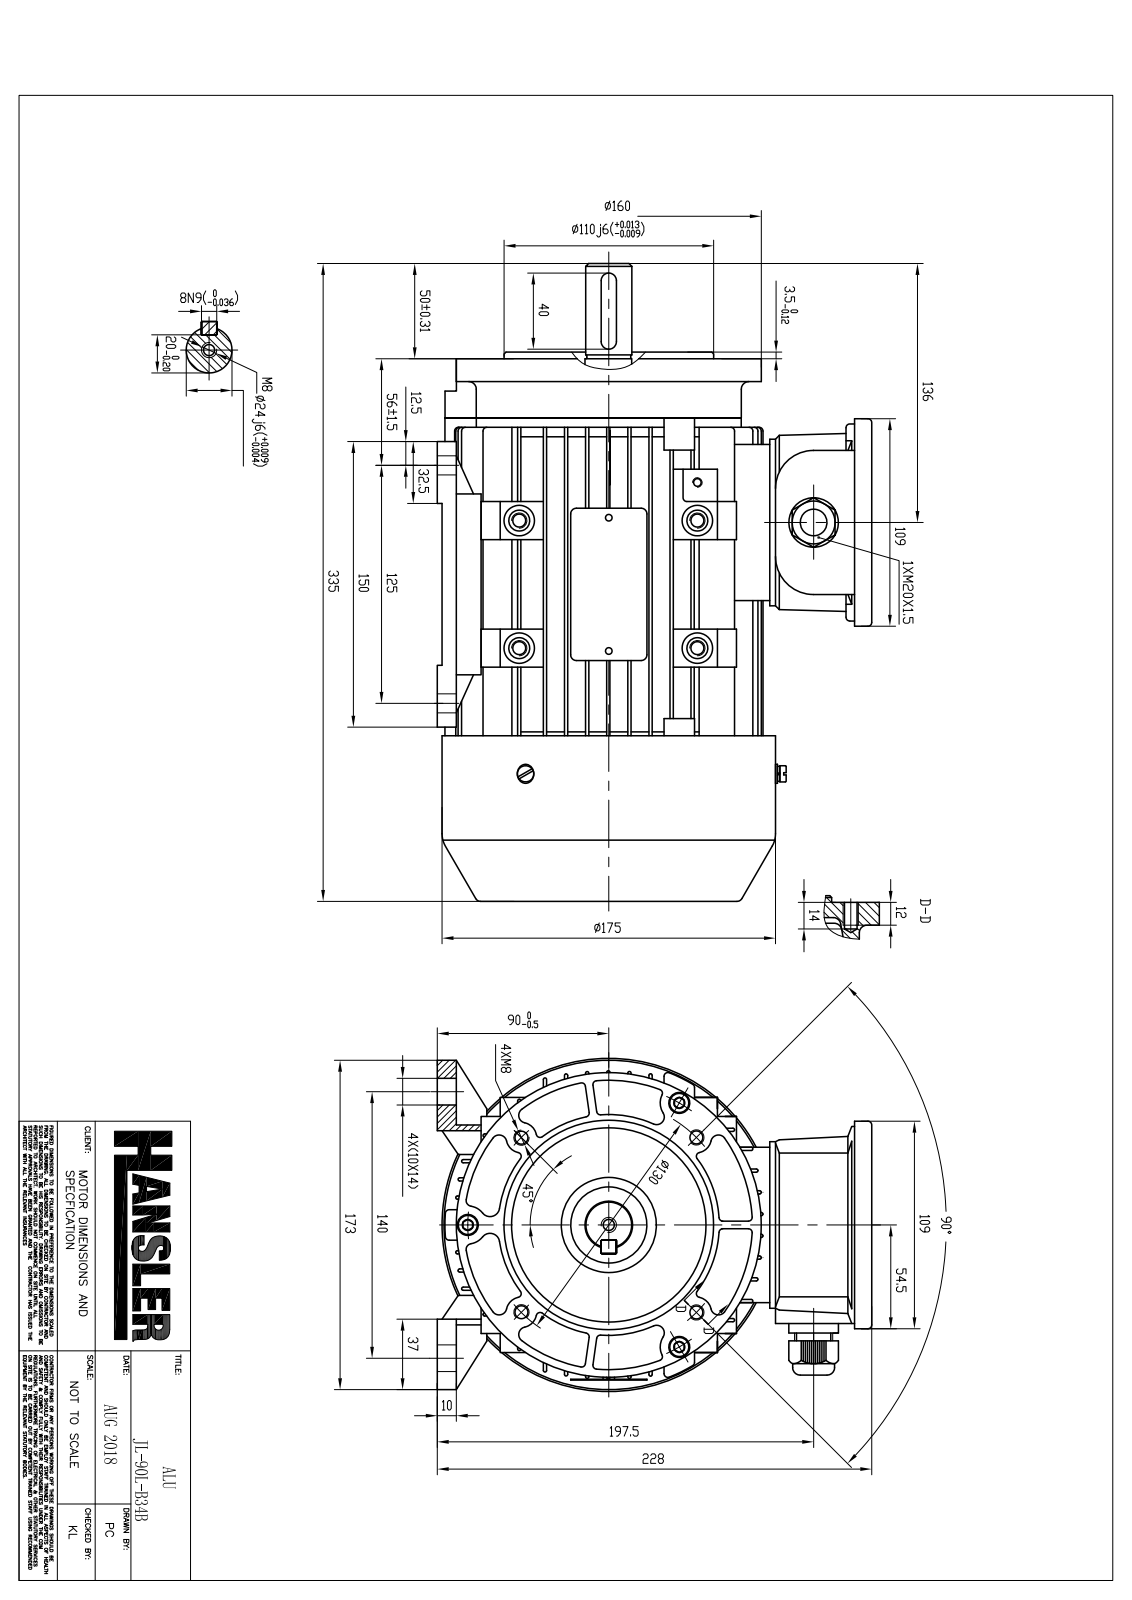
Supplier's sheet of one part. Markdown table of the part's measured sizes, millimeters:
| quantity | value |
| --- | --- |
| part name | JL-90L-B34B |
| STEP written by | SIEMENS PLM Software NX 12.0 (AP203_CONFIGURATION_CONTROLLED_3D_DESIGN_OF_MECHANICAL_PARTS_AND_ASSEMBLIES_MIM_LF) |
| units | millimeters |
| bodies | 51 solids, 4428 faces (2724 planar, 1317 cylindrical, 387 other) |
| overall size | 335 × 230.5 × 175 |
| volume | 1 440 000 mm³ |
| surface area | 907 832 mm² |
| round holes (diameter × count) | 8 × 14, 4 × 13, 5 × 11, 5.8 × 10, 16 × 8, 4.8 × 4, 5.25 × 4, 5.3 × 4, 8.58 × 4, 9 × 4, 12 × 4, 6 × 3 |
| round bosses / shafts (diameter × count) | 11 × 8, 4.48 × 8, 10 × 7, 15 × 4, 14.79 × 4, 13 × 4, 12 × 4, 7.85 × 4 |
| partial cylindrical surfaces (radius × count) | 0.5 × 464, 1 × 72, 2 × 70, 4 × 27, 5 × 18, 0.75 × 16, 1.5 × 14, 3 × 13 |
| main face-to-face distances | 1.7, 11.08, 44.32, 22.16, 5, 2.5, 9.38, 2, 33.24, 55.4 |
| hole center spacings | 35.51, 50.8, 57.1, 72.54, 77.07, 22, 15, 15.56 |
